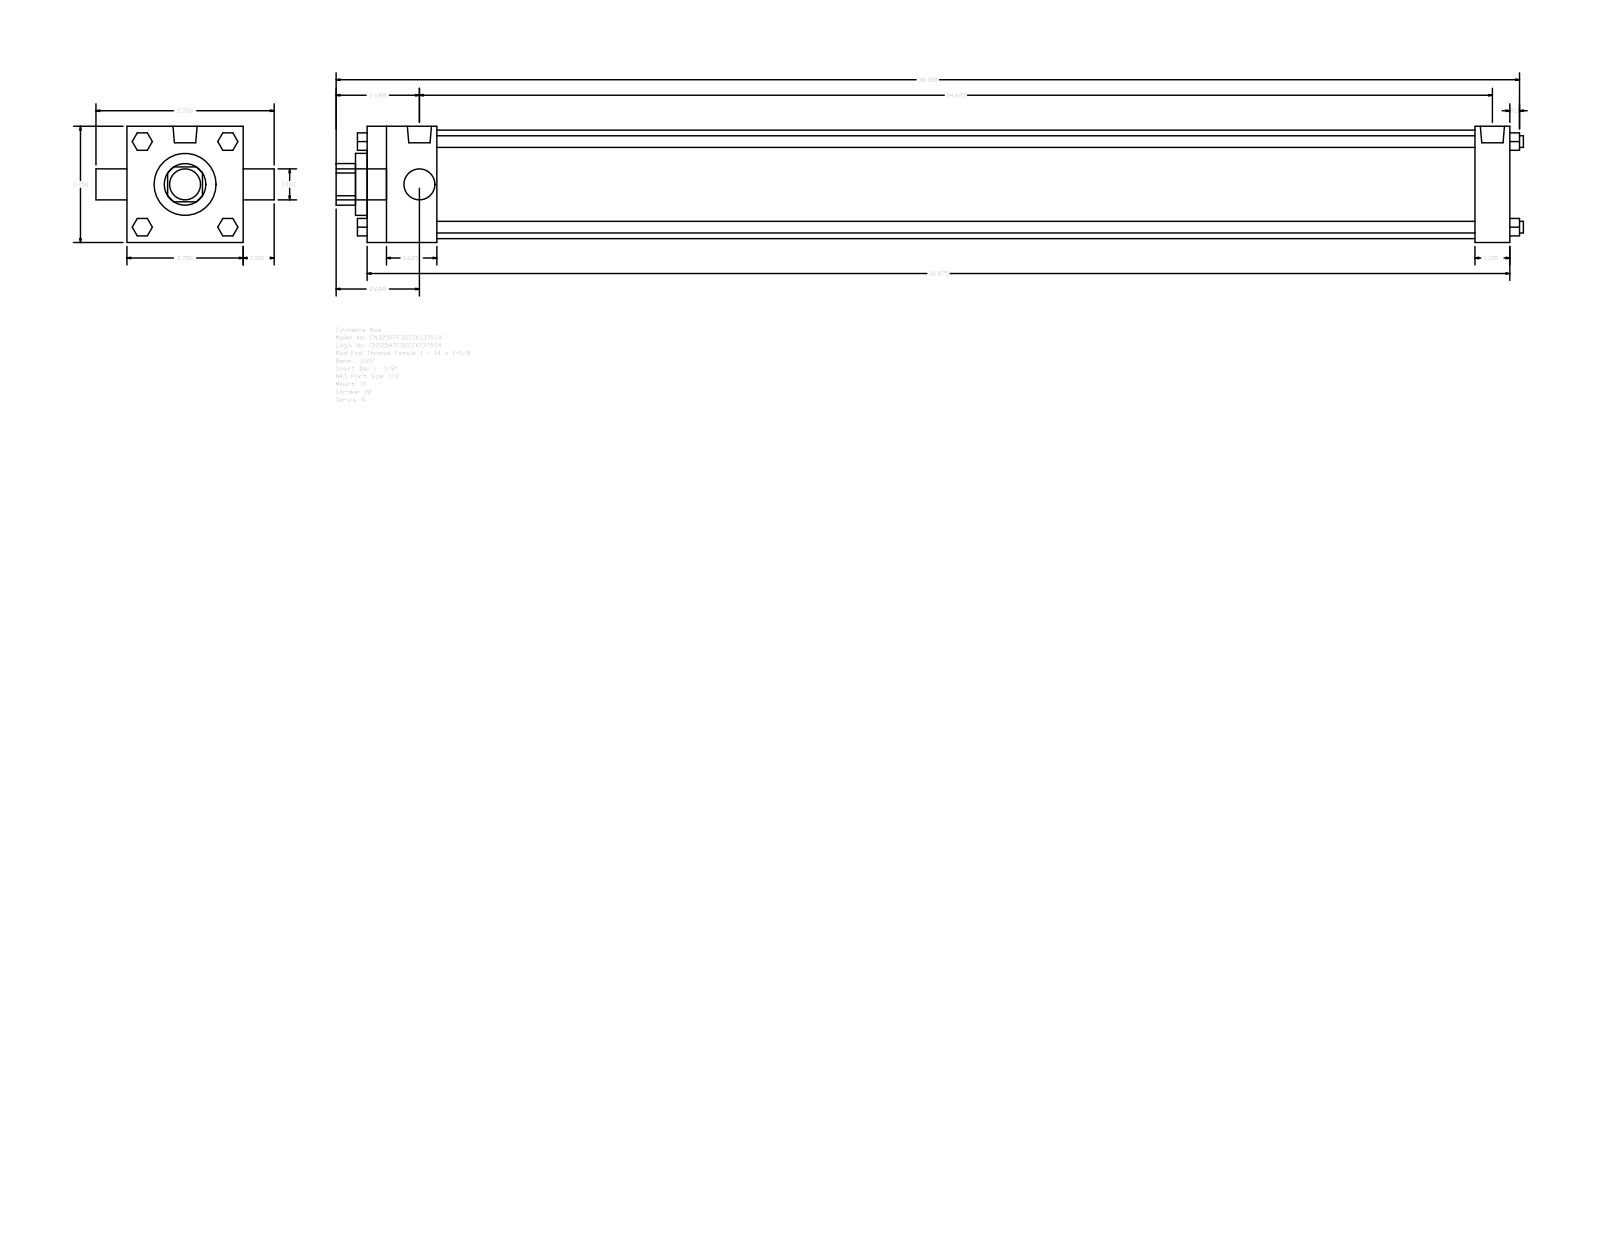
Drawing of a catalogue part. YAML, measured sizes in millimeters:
part_name: "A_TF__0325_1.375"
step_written_by: "GSSL Pune (CONFIG_CONTROL_DESIGN)"
units: millimeters
bodies: {solids: 0, faces: 120, planar: 92, cylindrical: 28, other: 0}
overall_size: [973.14, 146.05, 95.25]
round_holes:
  - {diameter: 25.4, count: 1}
  - {diameter: 34.92, count: 1}
  - {diameter: 50.8, count: 1}
  - {diameter: 88.9, count: 1}
round_bosses_or_shafts:
  - {diameter: 9.53, count: 4}
  - {diameter: 8.73, count: 3}
  - {diameter: 19.77, count: 2}
  - {diameter: 25.4, count: 1}
partial_cylinders:
  - {radius: 17.06, count: 1}
face_to_face_distances: [95.24, 936.62, 28.57, 57.15, 908.05, 850.9, 879.47, 9.52, 66.67, 917.57]
